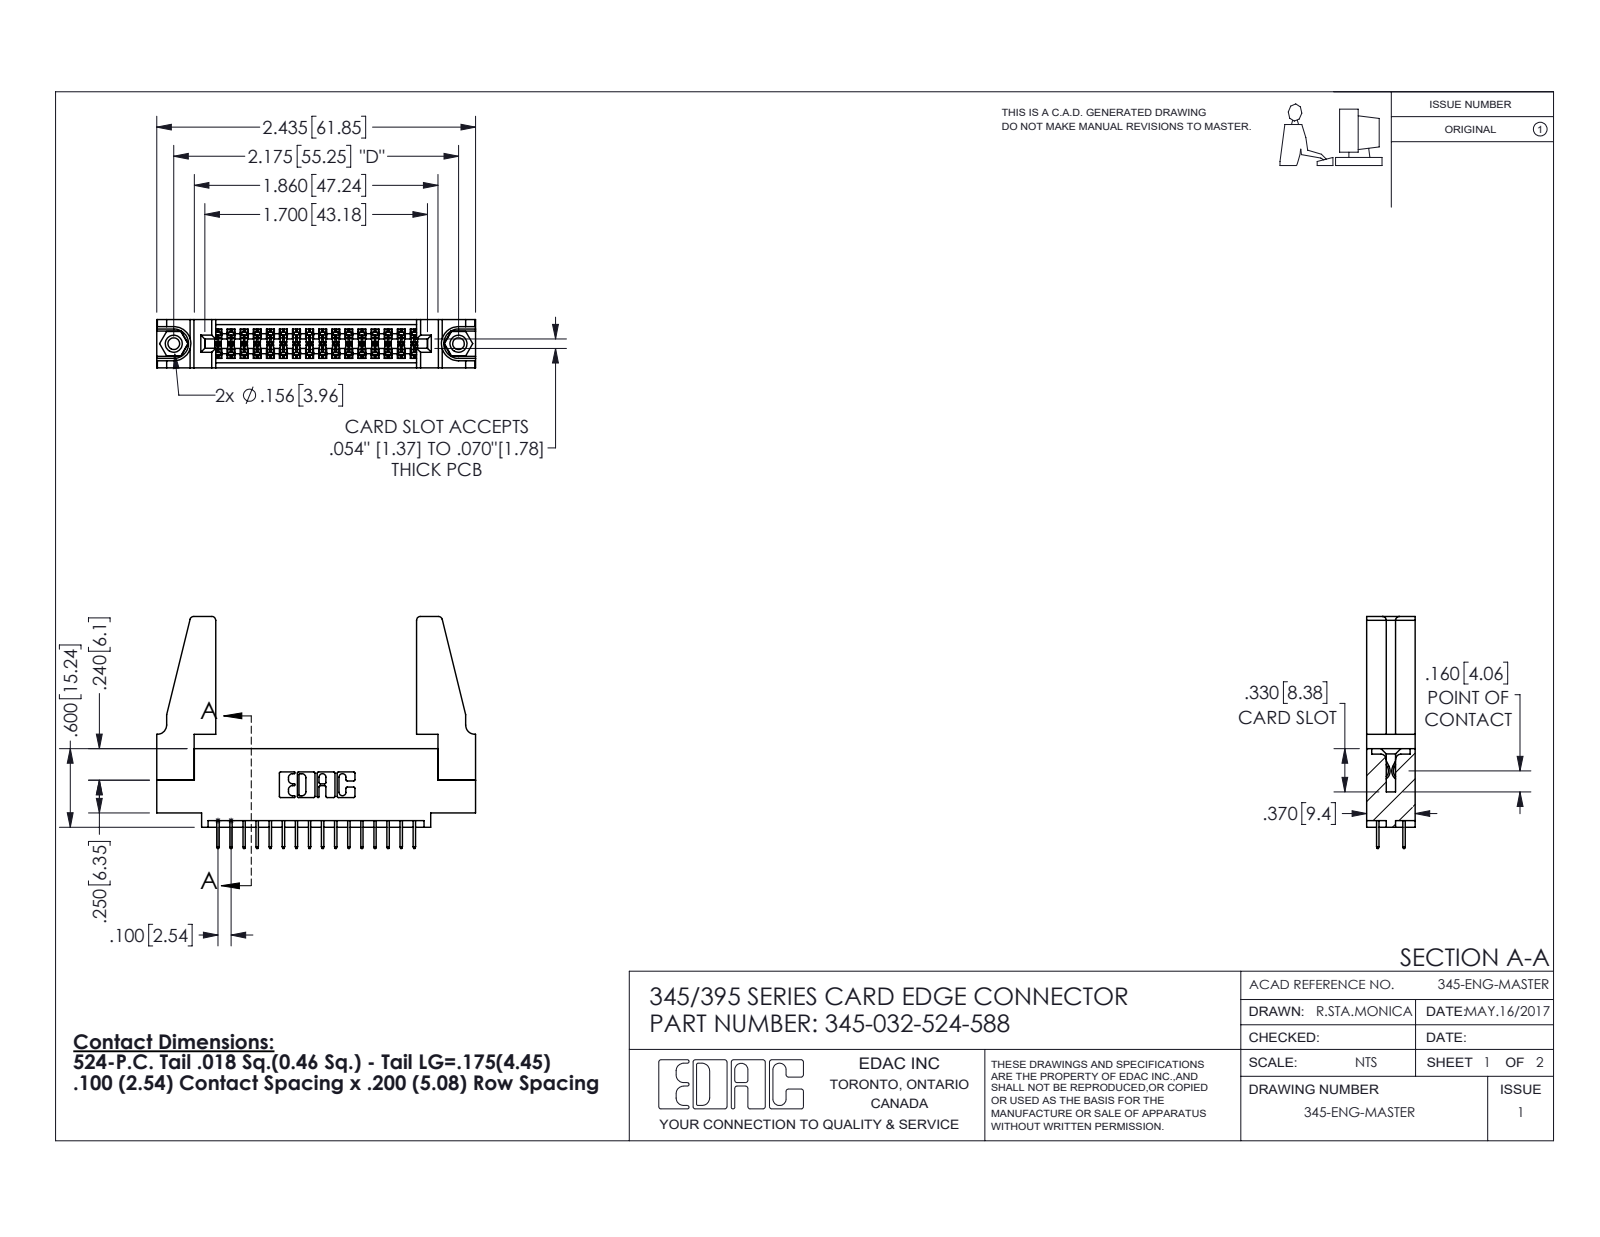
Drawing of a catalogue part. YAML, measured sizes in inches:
part_name: "345 Part_0.110 Offset - 0.156 Dia-TH; 345-032-524-588; 345-250-001_345-250-001-102; 345-292-001_345-293-124 (+1 more)"
step_written_by: "SolidWorks 2016 (CONFIG_CONTROL_DESIGN)"
units: inches
bodies: {solids: 37, faces: 1982, planar: 1404, cylindrical: 562, other: 16}
overall_size: [2.436, 1.772, 0.37]
volume: 0.543
surface_area: 16.94
round_holes:
  - {diameter: 0.089, count: 2}
  - {diameter: 0.125, count: 2}
  - {diameter: 0.156, count: 2}
  - {diameter: 0.064, count: 1}
round_bosses_or_shafts:
  - {diameter: 0.155, count: 2}
partial_cylinders:
  - {radius: 0.006, count: 48}
  - {radius: 0.01, count: 22}
  - {radius: 0.03, count: 8}
  - {radius: 0.007, count: 6}
  - {radius: 0.031, count: 6}
  - {radius: 0.026, count: 3}
  - {radius: 0.014, count: 2}
  - {radius: 0.019, count: 2}
face_to_face_distances: [0.37, 0.072, 0.298, 0.2, 0.098, 0.272, 0.025, 0.225, 0.072, 0.148]
hole_center_spacings: [0.27, 1.942, 2.175]
